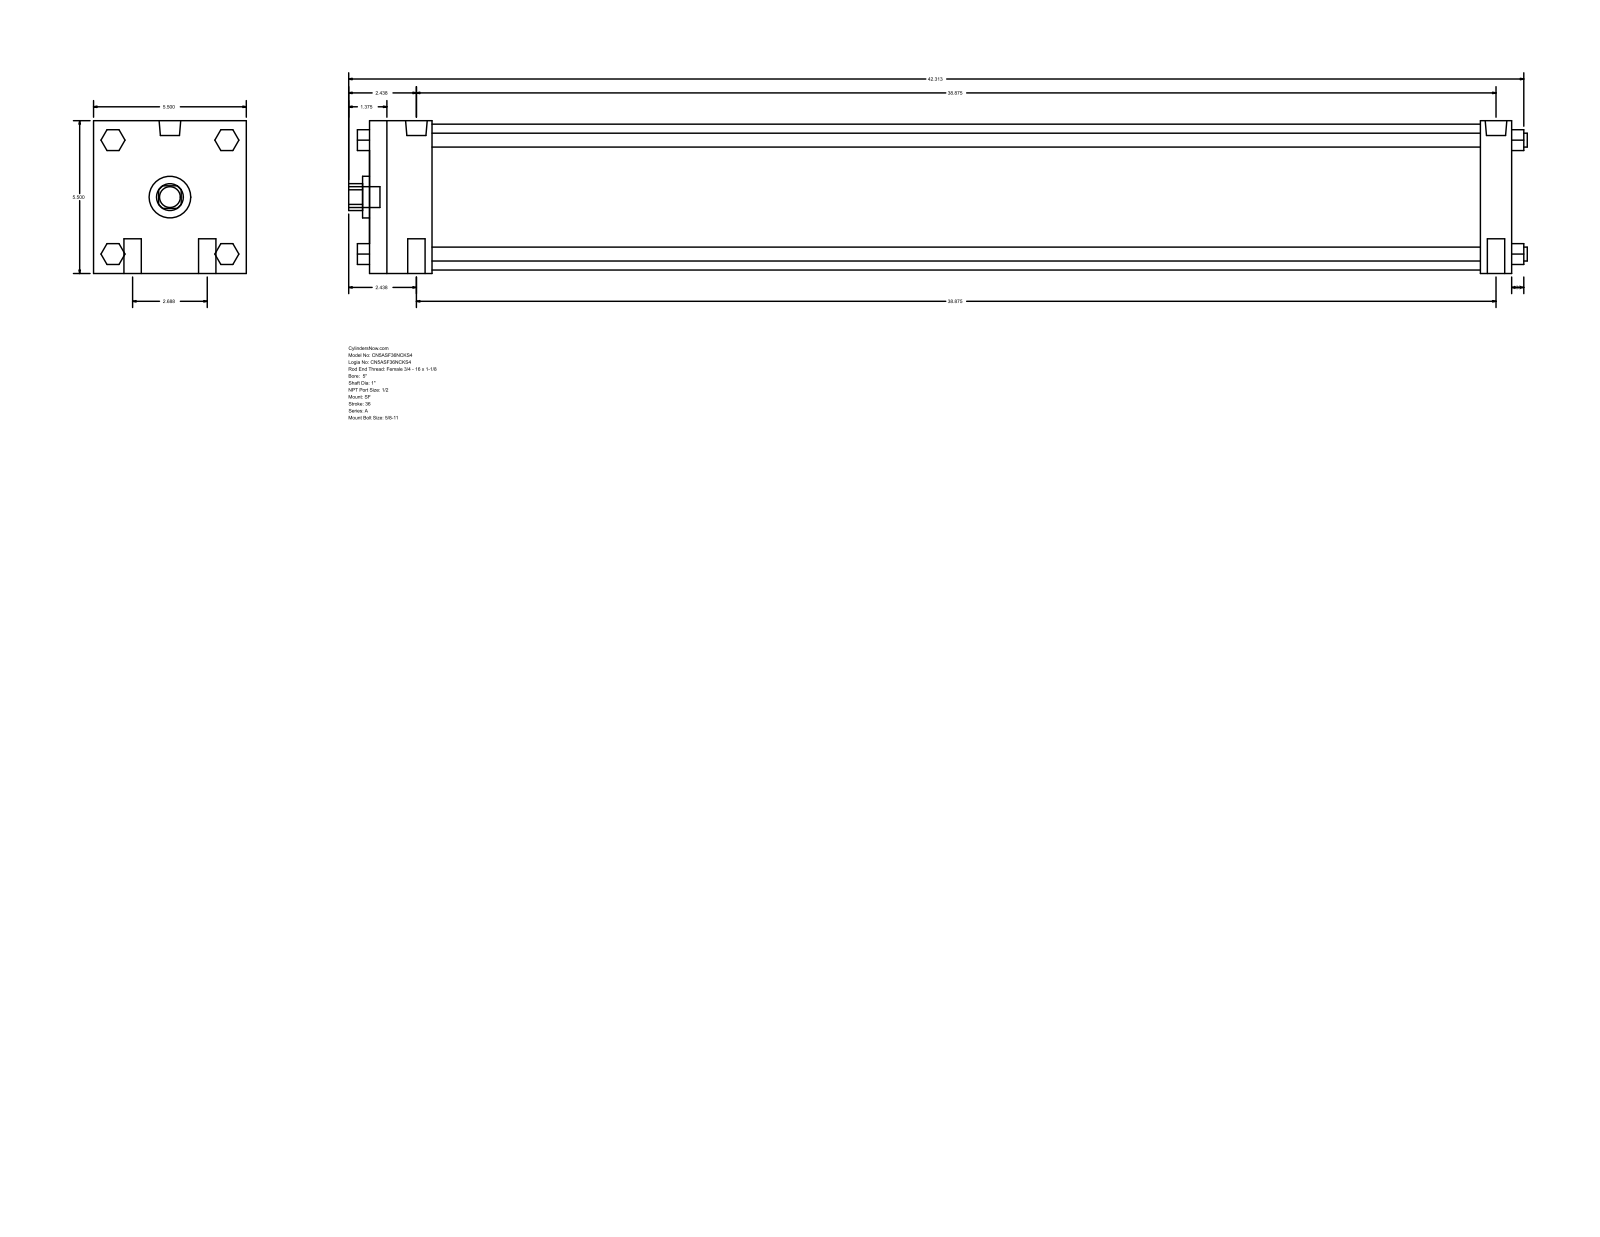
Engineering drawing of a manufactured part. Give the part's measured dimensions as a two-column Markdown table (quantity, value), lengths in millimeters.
| quantity | value |
| --- | --- |
| part name | A_SF__0500_1 |
| STEP written by | GSSL Pune (CONFIG_CONTROL_DESIGN) |
| units | millimeters |
| bodies | 0 solids, 124 faces (94 planar, 30 cylindrical, 0 other) |
| overall size | 1077.91 × 139.7 × 139.7 |
| round holes (diameter × count) | 25.4 × 1, 38.1 × 1, 133.35 × 1 |
| round bosses / shafts (diameter × count) | 15.88 × 4, 12.7 × 4, 19.77 × 2, 8.73 × 2, 19.05 × 1 |
| partial cylindrical surfaces (radius × count) | 12.29 × 1 |
| main face-to-face distances | 139.7, 1044.57, 28.57, 57.15, 1016, 958.85, 987.42, 19.05, 52.07, 90.18 |
